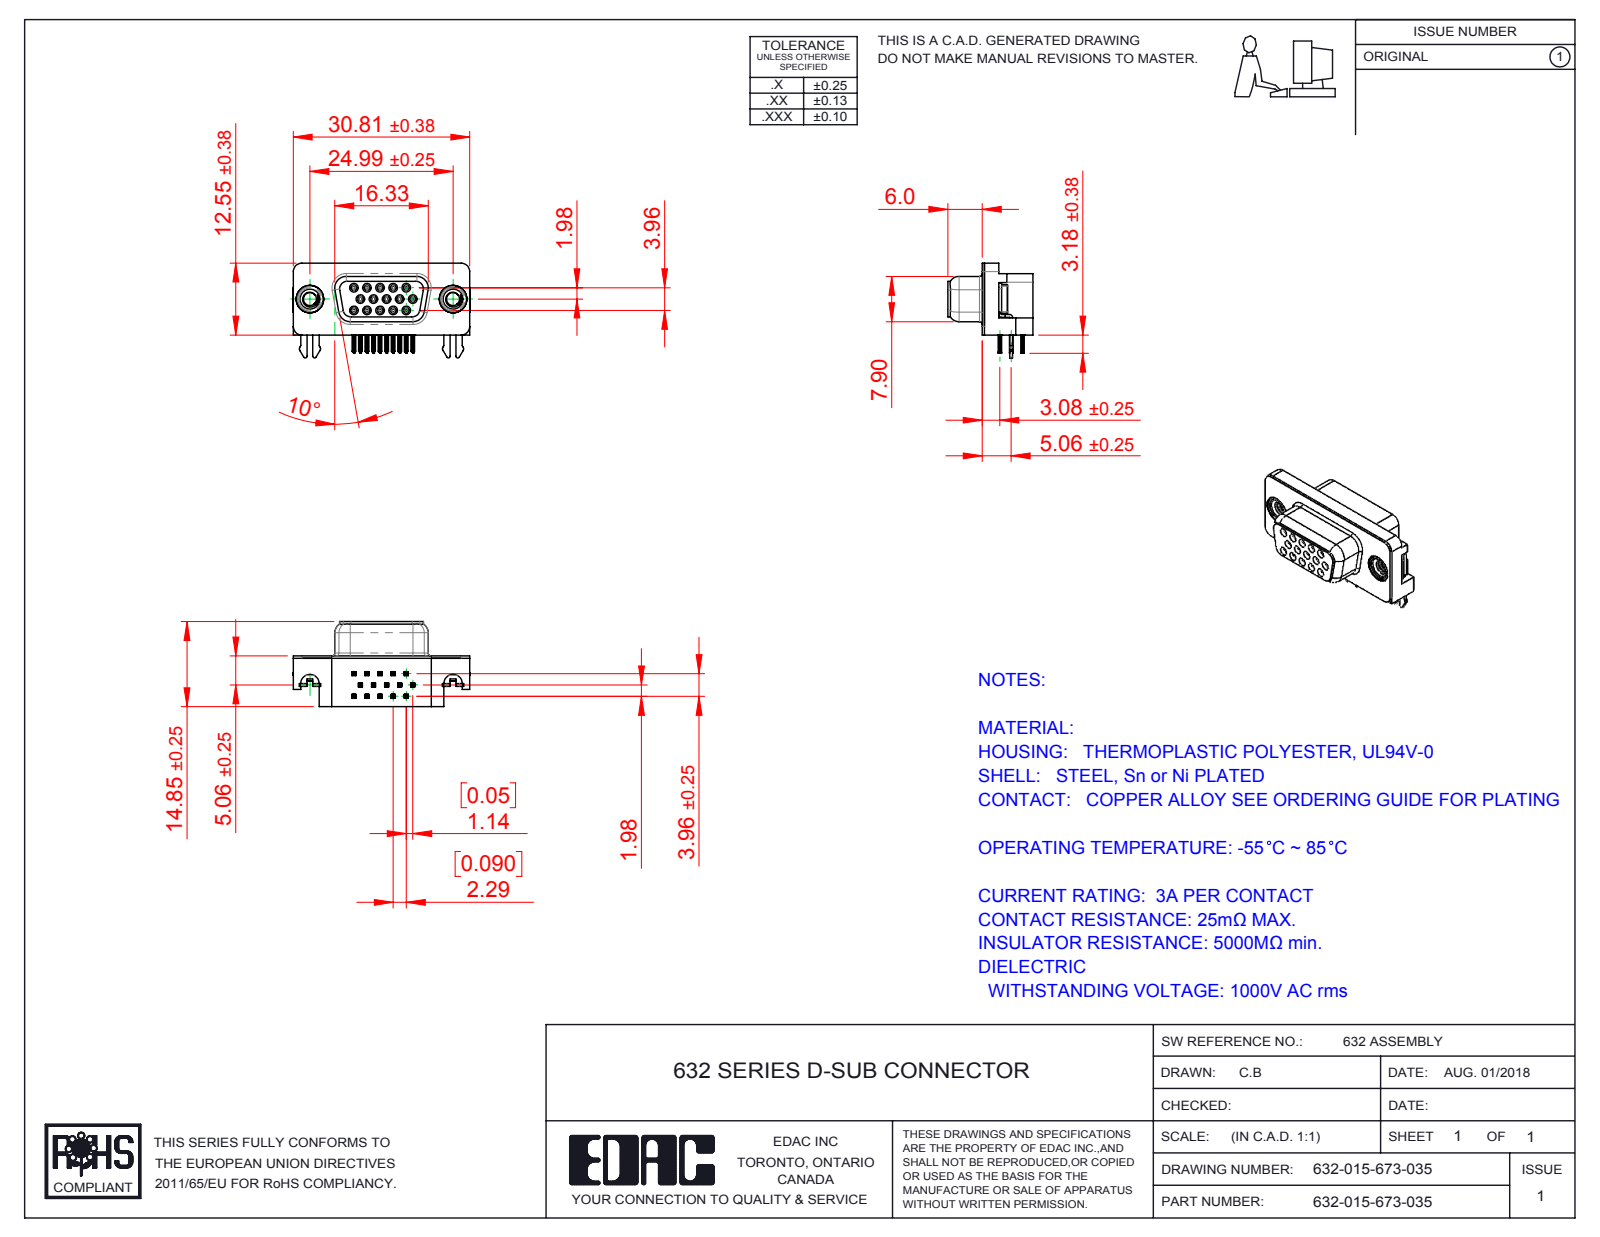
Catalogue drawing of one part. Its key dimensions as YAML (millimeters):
part_name: "632 M3 Threaded Rivet; 632 4-40 Threaded Rivet; 632 2 Prong Board Lock; 632-015-673-035 (+6 more)"
step_written_by: "SolidWorks 2016 (CONFIG_CONTROL_DESIGN)"
units: millimeters
bodies: {solids: 23, faces: 2426, planar: 1006, cylindrical: 654, other: 766}
overall_size: [30.89, 16.55, 14.85]
volume: 2996
surface_area: 5339
round_holes:
  - {diameter: 0.8, count: 15}
  - {diameter: 0.9, count: 15}
  - {diameter: 2.26, count: 2}
  - {diameter: 2.5, count: 2}
  - {diameter: 4, count: 2}
  - {diameter: 4.8, count: 2}
  - {diameter: 5, count: 2}
round_bosses_or_shafts:
  - {diameter: 1.2, count: 15}
  - {diameter: 4.9, count: 2}
  - {diameter: 4.75, count: 2}
  - {diameter: 3.9, count: 2}
partial_cylinders:
  - {radius: 0.1, count: 120}
  - {radius: 0.15, count: 60}
  - {radius: 0.35, count: 30}
  - {radius: 0.34, count: 15}
  - {radius: 1, count: 11}
  - {radius: 0.28, count: 10}
  - {radius: 0.5, count: 10}
  - {radius: 0.25, count: 8}
face_to_face_distances: [0.4, 8.45, 8.85, 1.98, 2.9, 5.95, 2.5, 6.4, 6.7, 7.05]
hole_center_spacings: [2.28, 2.29, 3.96, 4.57, 6.05, 3.97, 4.58, 6.86]
